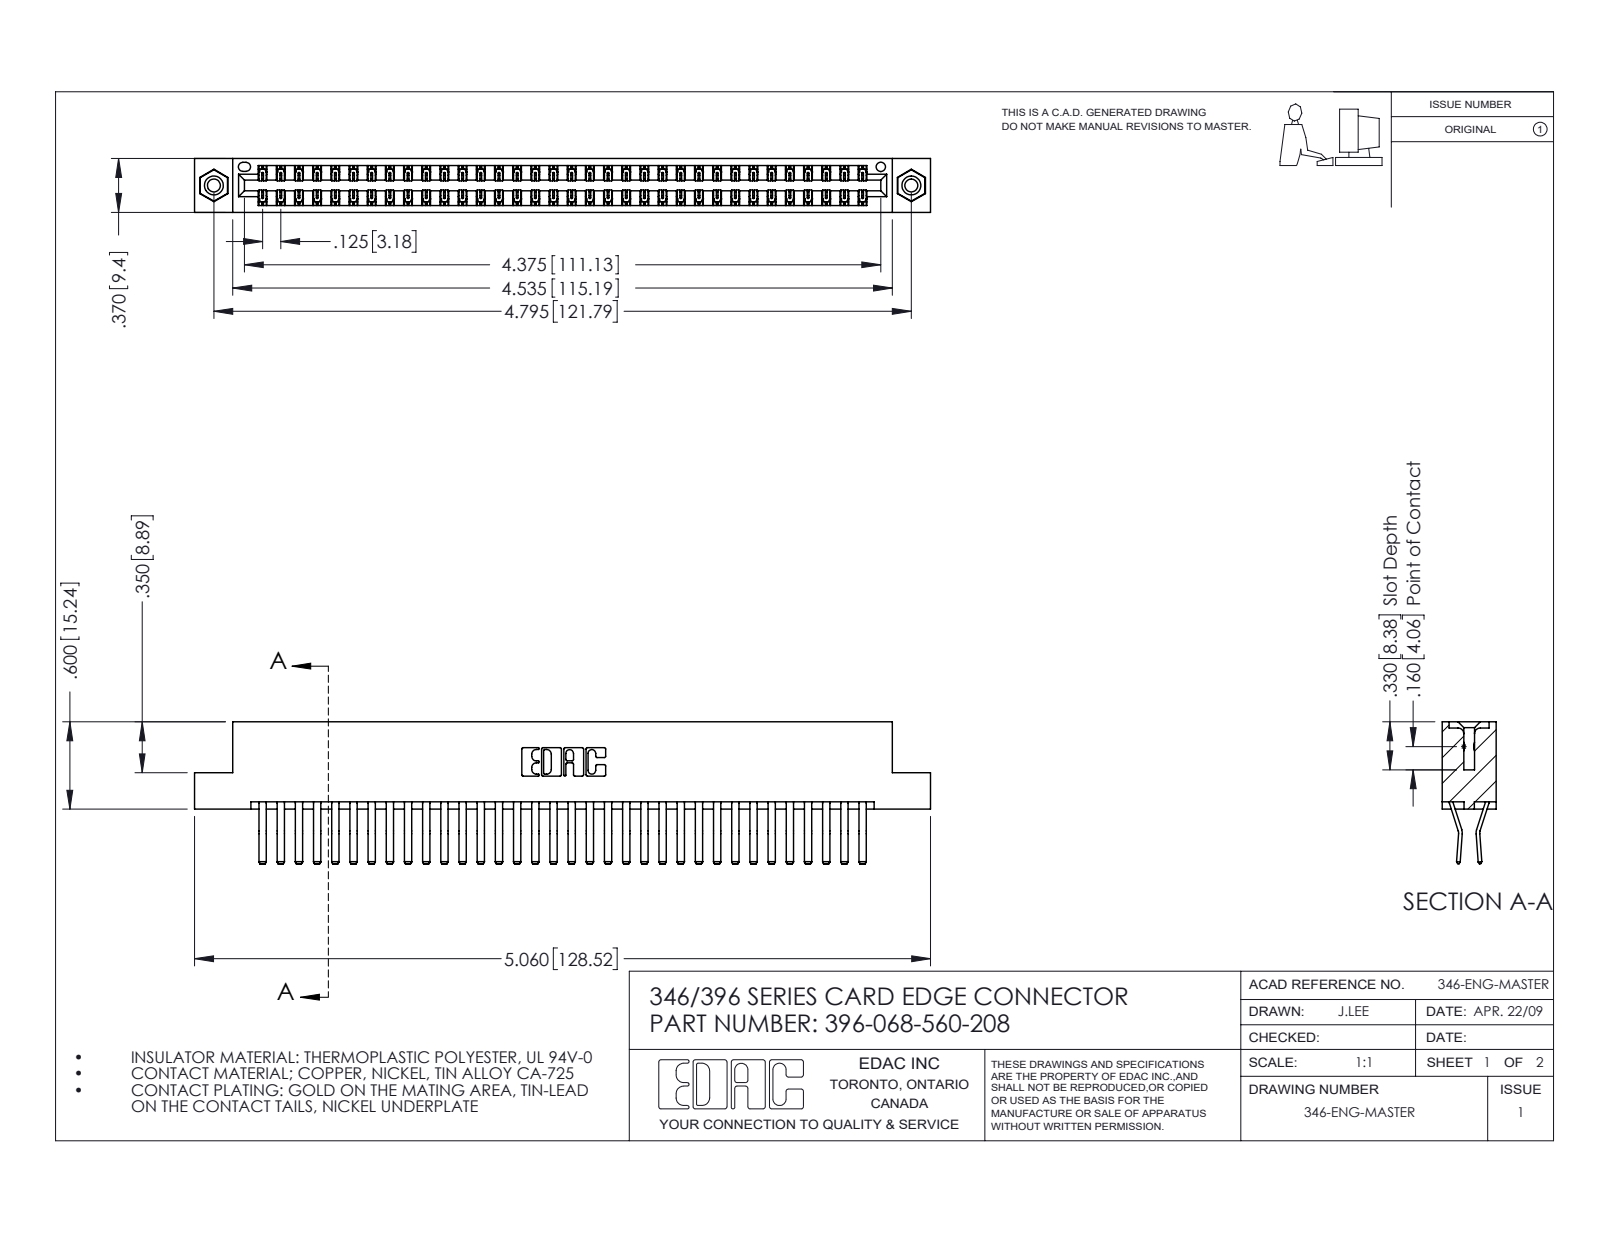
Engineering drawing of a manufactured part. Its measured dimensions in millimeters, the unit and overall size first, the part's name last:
Units: millimetres
Overall size (bounding box): 128.5 × 24.8 × 9.4
Round holes (diameter × count): ⌀2.3 ×2, ⌀3.2 ×2, ⌀4 ×2, ⌀1.6 ×1
Round bosses / shafts (diameter × count): ⌀3.9 ×2
Partial cylindrical surfaces — rounded edges, fillets, slot ends (radius × count): R0.2 ×102, R0.3 ×22, R0.2 ×6, R0.8 ×6, R0.7 ×3, R0.3 ×2, R0.4 ×2, R0.6 ×2
Main face-to-face distances: 1.2, 8.2, 9.4, 0.6, 6.4, 1.8, 7.6, 7, 3.8, 5.6
Hole centre spacings: 6.2, 116.5, 121.8
Volume: 12 900 mm³ · Surface area: 18 830 mm²
Bodies: 71 solids, 3854 faces (2488 planar, 1350 cylindrical, 16 other)
Part name (STEP PRODUCT): 346 Part_Flush Mounting Lugs - 0.156 Dia-TI; 396-068-560-208; 345-250-001_345-250-003-102; 345-292-001_560 Tail
STEP written by: SolidWorks 2016 (CONFIG_CONTROL_DESIGN)
